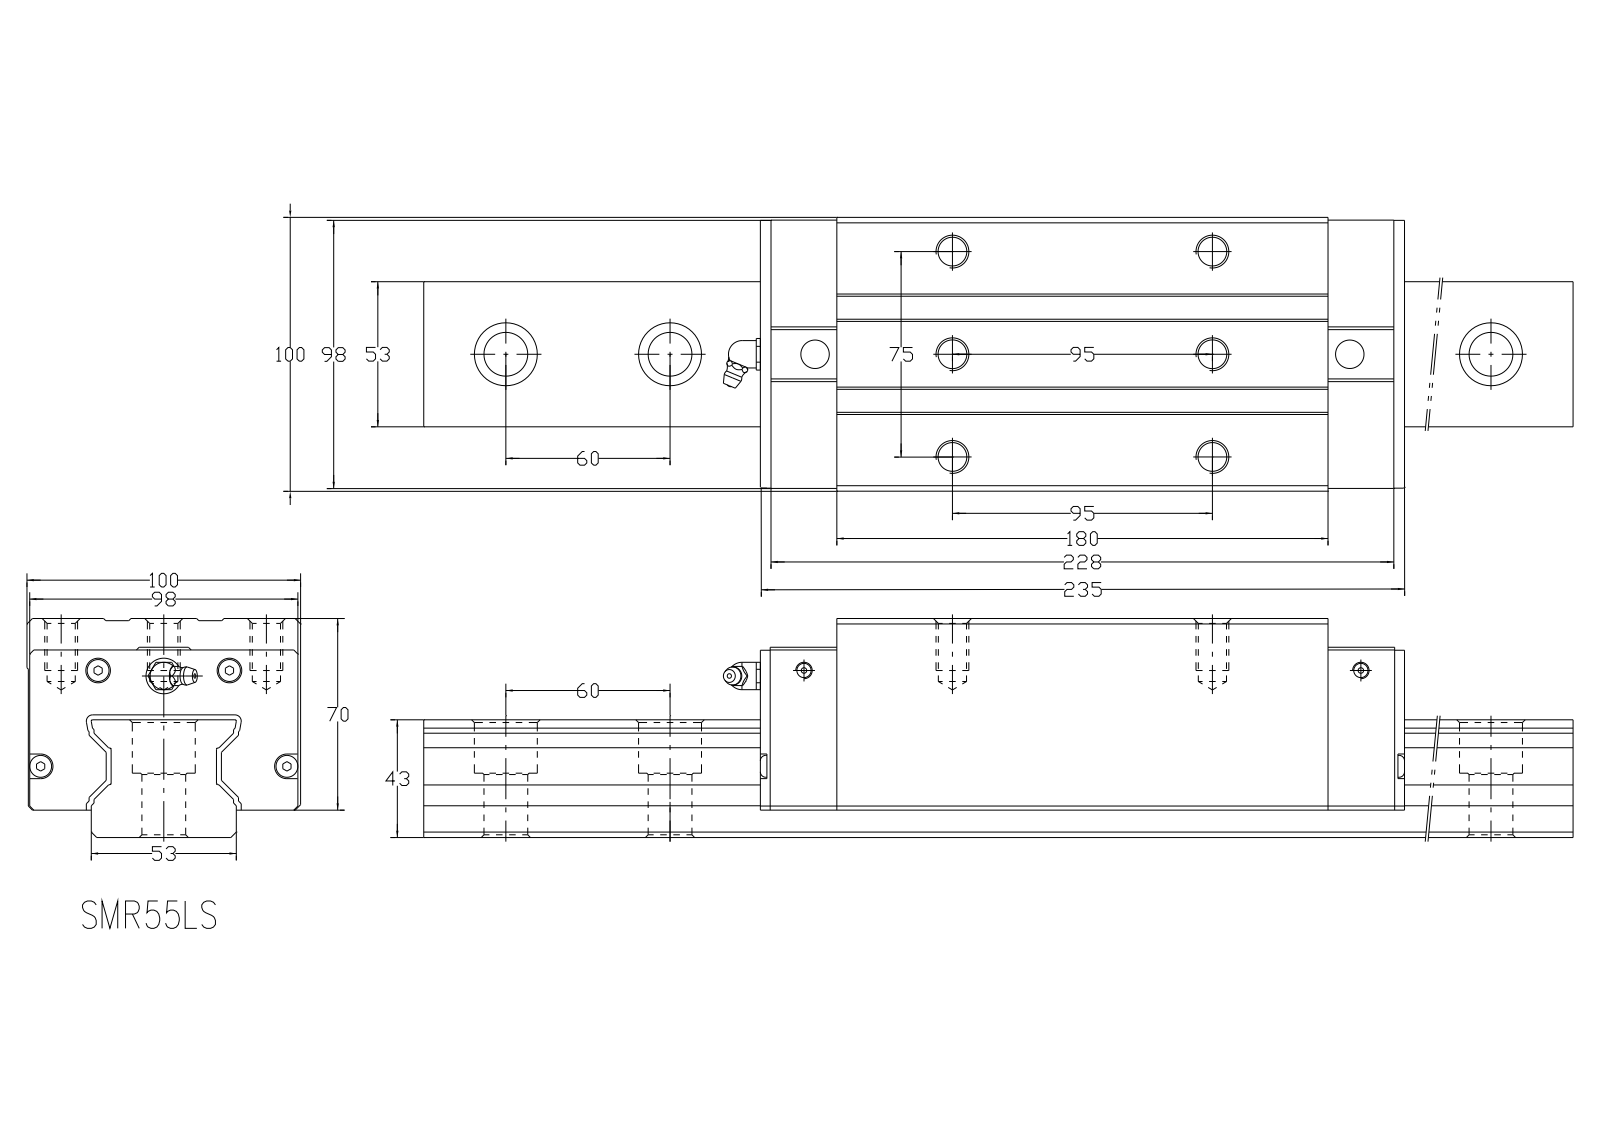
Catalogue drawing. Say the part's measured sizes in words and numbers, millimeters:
Its 3-D file was written by "Kubotek KeyCreator V6.5.2 (0407) (CONFIG_CONTROL_DESIGN)". It is 7 solids with 990 faces: 725 planar, 180 cylindrical and 85 other. Overall it measures 350 by 100 by 80 millimeters. Its volume is 1 845 000 cubic millimeters and its surface area 230 956 square millimeters. Round holes: 6 of diameter 10.9, 4 of diameter 16, 4 of diameter 23, 2 of diameter 2, 2 of diameter 9, 2 of diameter 10.4, 1 of diameter 13. Round bosses or shafts: 1 of diameter 10. Partial cylindrical surfaces (rounded edges, fillets, slot ends): 42 of radius 0.2, 16 of radius 0.85, 8 of radius 0.35, 6 of radius 0.5, 4 of radius 0.55, 2 of radius 0.45, 2 of radius 1.04, 2 of radius 1.5. The main face-to-face distances are 43, 80, 37, 23.5, 30.75, 69.25, 10, 179.5, 33, 70. The hole center spacings are 37.5, 62.66, 102.13, 149.96, 95, 24.08, 50.08, 50.2.
